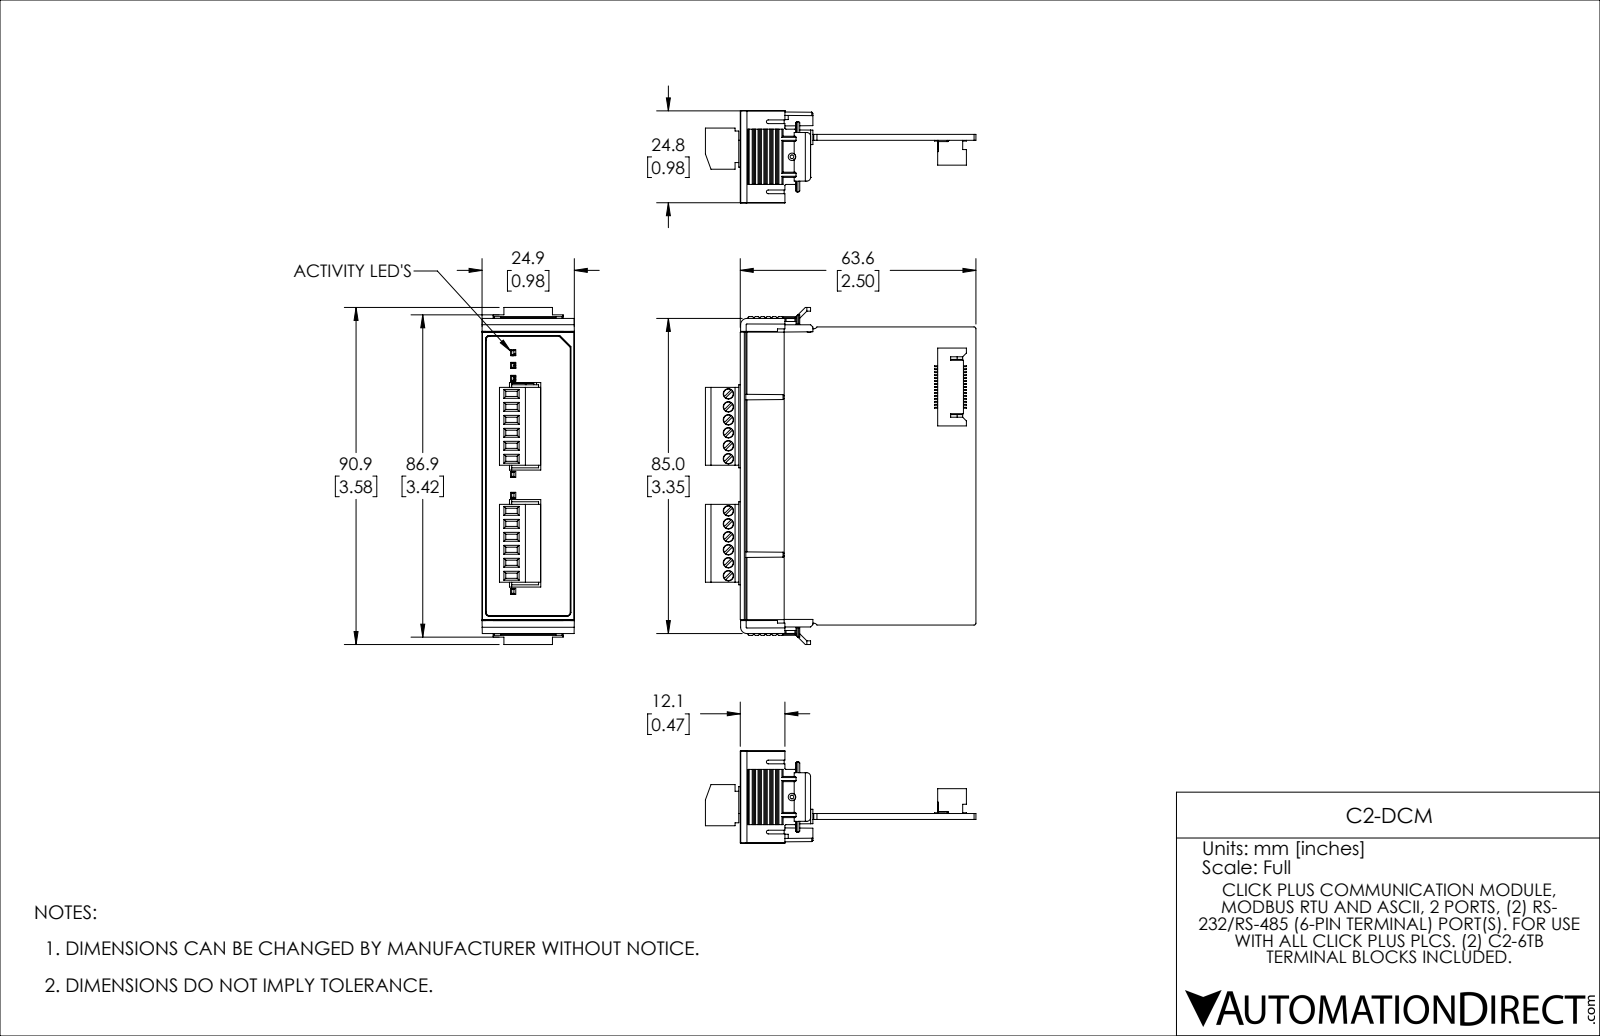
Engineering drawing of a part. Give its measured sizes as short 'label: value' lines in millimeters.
name: C2-DCM
written by: SolidWorks 2021 (AUTOMOTIVE_DESIGN)
unit: mm
bodies: 16 solids, 2102 faces (1866 planar, 213 cylindrical, 23 other)
size: 90.9 × 73 × 24.9
volume: 20 910 mm³; area: 34 050 mm²
holes: 12× ⌀1, 12× ⌀1.2, 12× ⌀2.8
bosses: 24× ⌀0.8, 12× ⌀2.6, 2× ⌀0.6
rounds: 52× R0.3, 16× R1, 12× R2.8, 12× R2.8, 10× R0.5, 4× R0.1, 4× R0.4, 2× R0.2
face distances: 1.6, 0.5, 1.7, 1, 21.6, 21.5, 0.4, 1.2, 1.5, 2.1
hole spacings: 3.5, 7, 11.4, 10.5, 31.5, 12.9, 28, 35.1
